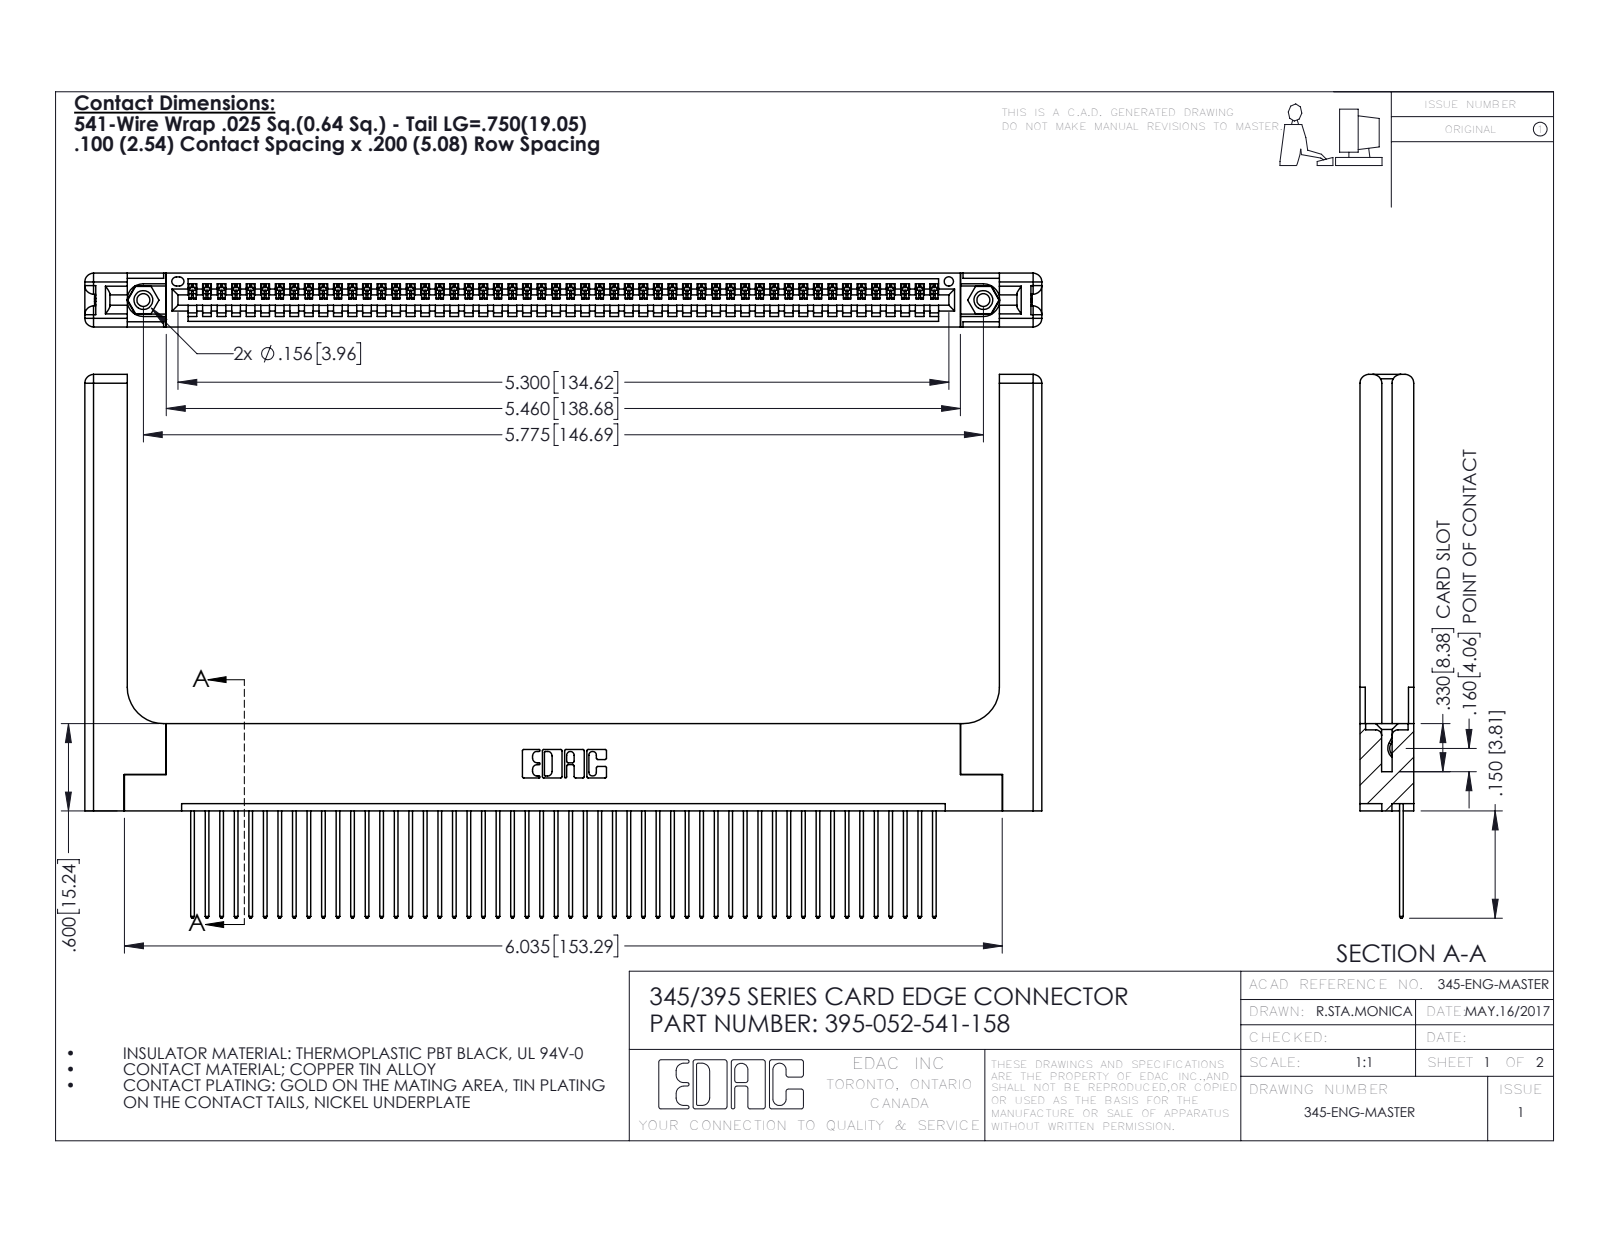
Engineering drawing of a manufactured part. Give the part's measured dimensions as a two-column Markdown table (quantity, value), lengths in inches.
| quantity | value |
| --- | --- |
| part name | 395-052-541-158; 345-292-001_345-293-141; 345 Part_Flush Mounting Lugs - 0.156 Dia-TH; 345-250-001_345-250-001-102 (+1 more) |
| STEP written by | SolidWorks 2016 (CONFIG_CONTROL_DESIGN) |
| units | inches |
| bodies | 57 solids, 3398 faces (2308 planar, 1030 cylindrical, 60 other) |
| overall size | 6.579 × 3.737 × 0.37 |
| volume | 1.503 in³ |
| surface area | 43.21 in² |
| round holes (diameter × count) | 0.089 × 2, 0.125 × 2, 0.156 × 2, 0.064 × 1 |
| round bosses / shafts (diameter × count) | 0.155 × 2 |
| partial cylindrical surfaces (radius × count) | 0.006 × 104, 0.01 × 104, 0.01 × 22, 0.06 × 16, 0.007 × 6, 0.031 × 6, 0.026 × 3, 0.03 × 2 |
| main face-to-face distances | 0.072, 0.298, 0.37, 0.098, 0.272, 0.025, 0.2, 0.225, 0.148, 0.15 |
| hole center spacings | 0.27, 5.539, 5.775 |
